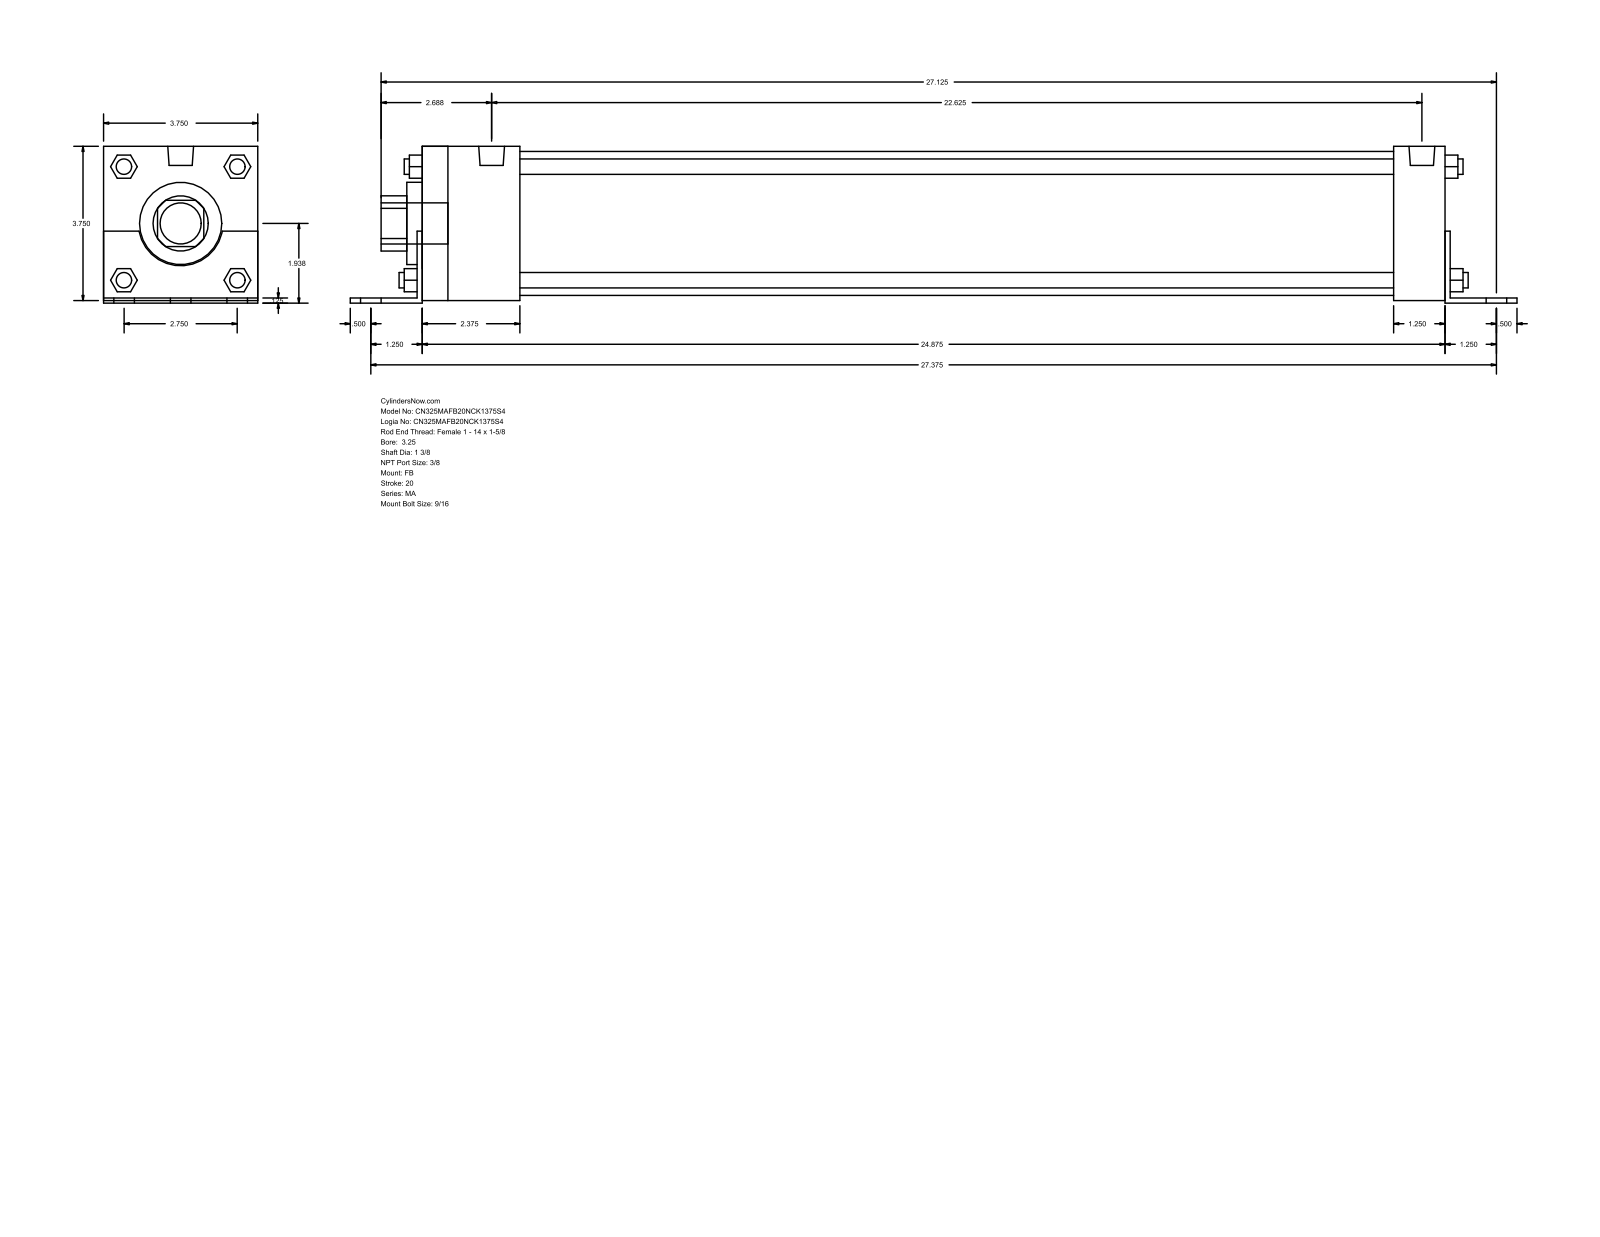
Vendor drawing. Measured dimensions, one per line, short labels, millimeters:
name: MA_FB__0325_1.375
written by: GSSL Pune (CONFIG_CONTROL_DESIGN)
unit: mm
bodies: 0 solids, 140 faces (105 planar, 35 cylindrical, 0 other)
size: 720.73 × 96.84 × 95.25
holes: 1× ⌀34.92, 1× ⌀50.8, 1× ⌀88.9
bosses: 6× ⌀14.29, 4× ⌀11.11, 4× ⌀9.53, 2× ⌀15.93, 1× ⌀25.4
rounds: 1× R17.06, 1× R26.16
face distances: 95.24, 3.17, 1.59, 96.83, 1.58, 93.66, 635, 631.83, 31.75, 60.32
